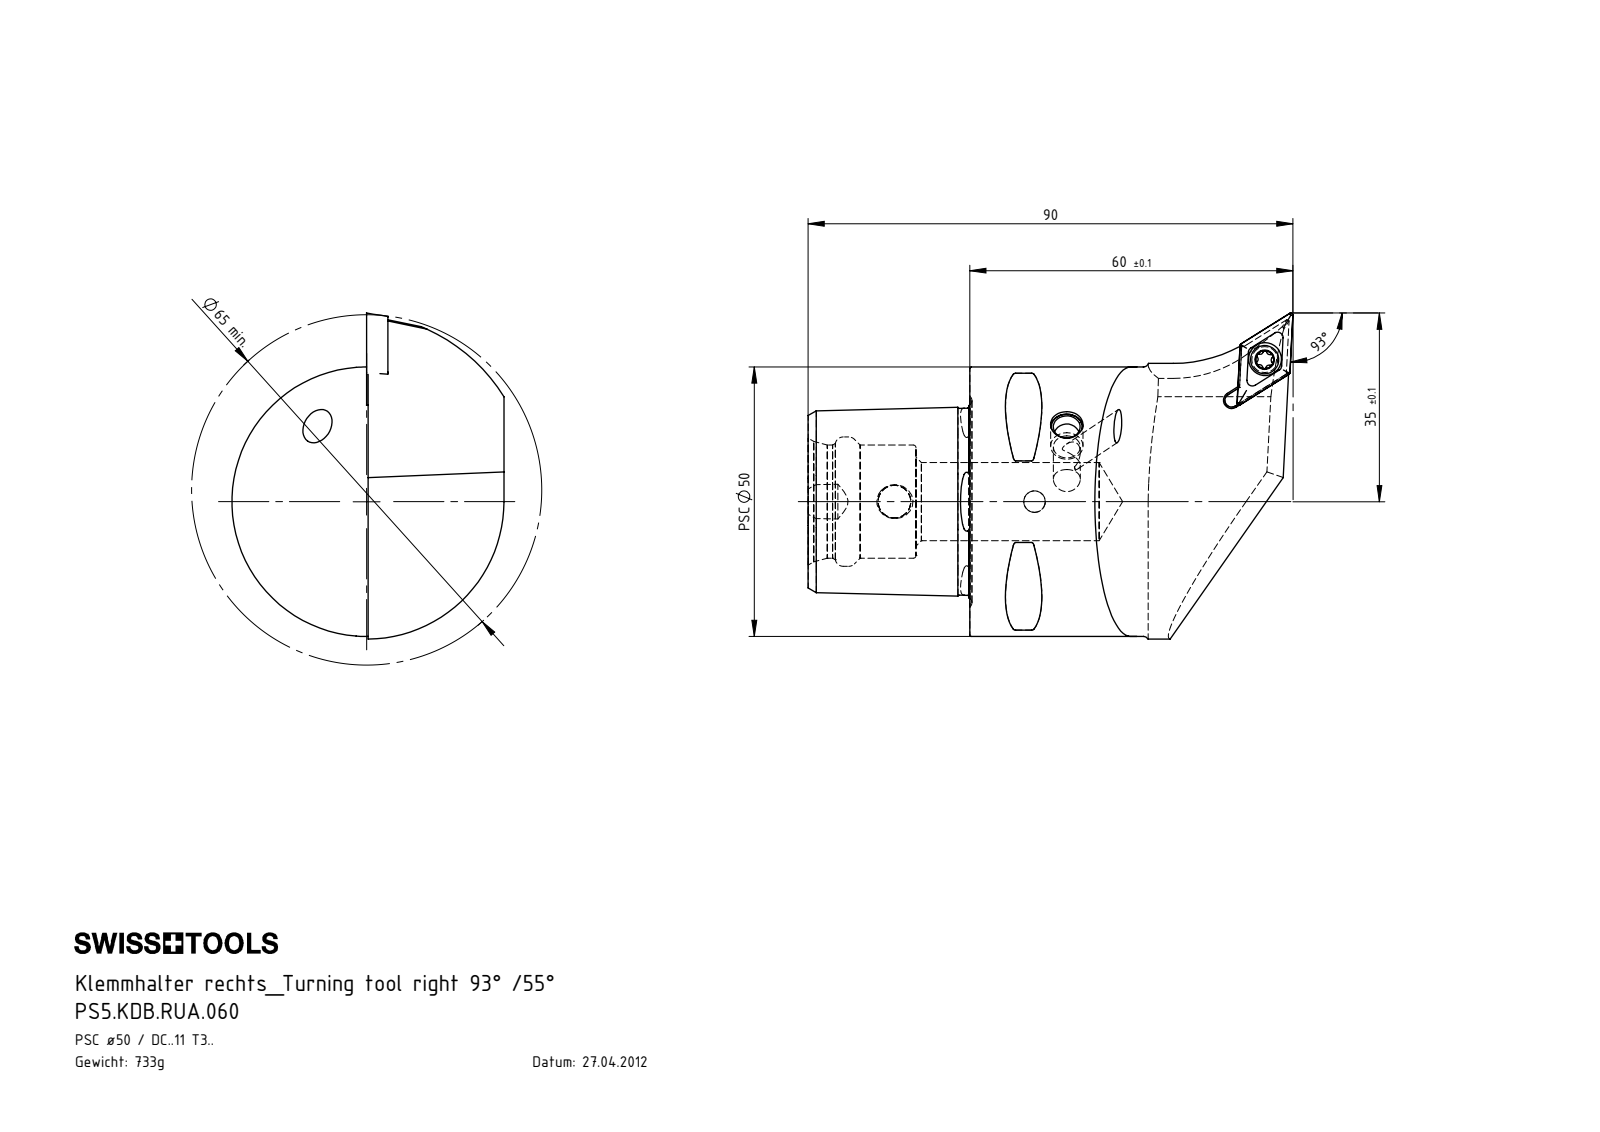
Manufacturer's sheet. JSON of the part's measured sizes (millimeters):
{"part_name": "WCB-ER2.001.009_A; KVT_MB_600_060; PS5-KDB.RUA.060_A; PS5.KDB.RUA.060 (+1 more)", "step_written_by": "SolidWorks 2017 (AUTOMOTIVE_DESIGN)", "units": "millimeters", "bodies": {"solids": 5, "faces": 199, "planar": 53, "cylindrical": 45, "other": 101}, "overall_size": [90, 60.5, 50.5], "volume_mm3": 93124, "surface_area_mm2": 19478, "round_holes": [[5, 3], [6.1, 2], [3.3, 1], [4, 1], [4.4, 1], [6, 1], [14.5, 1], [21, 1], [24, 1]], "round_bosses_or_shafts": [[50, 1], [6, 1], [5.25, 1], [4, 1]], "partial_cylinders_radius": [[0.5, 8], [0.34, 6], [0.59, 6], [1.25, 1], [3, 1], [4, 1], [25.5, 1], [26, 1]], "face_to_face_distances": [25.2, 30, 19.18, 21.53, 3.67, 44.4, 20, 10, 29.8, 9.8], "hole_center_spacings": [26, 50.21, 50.32, 73.62, 73.71]}
